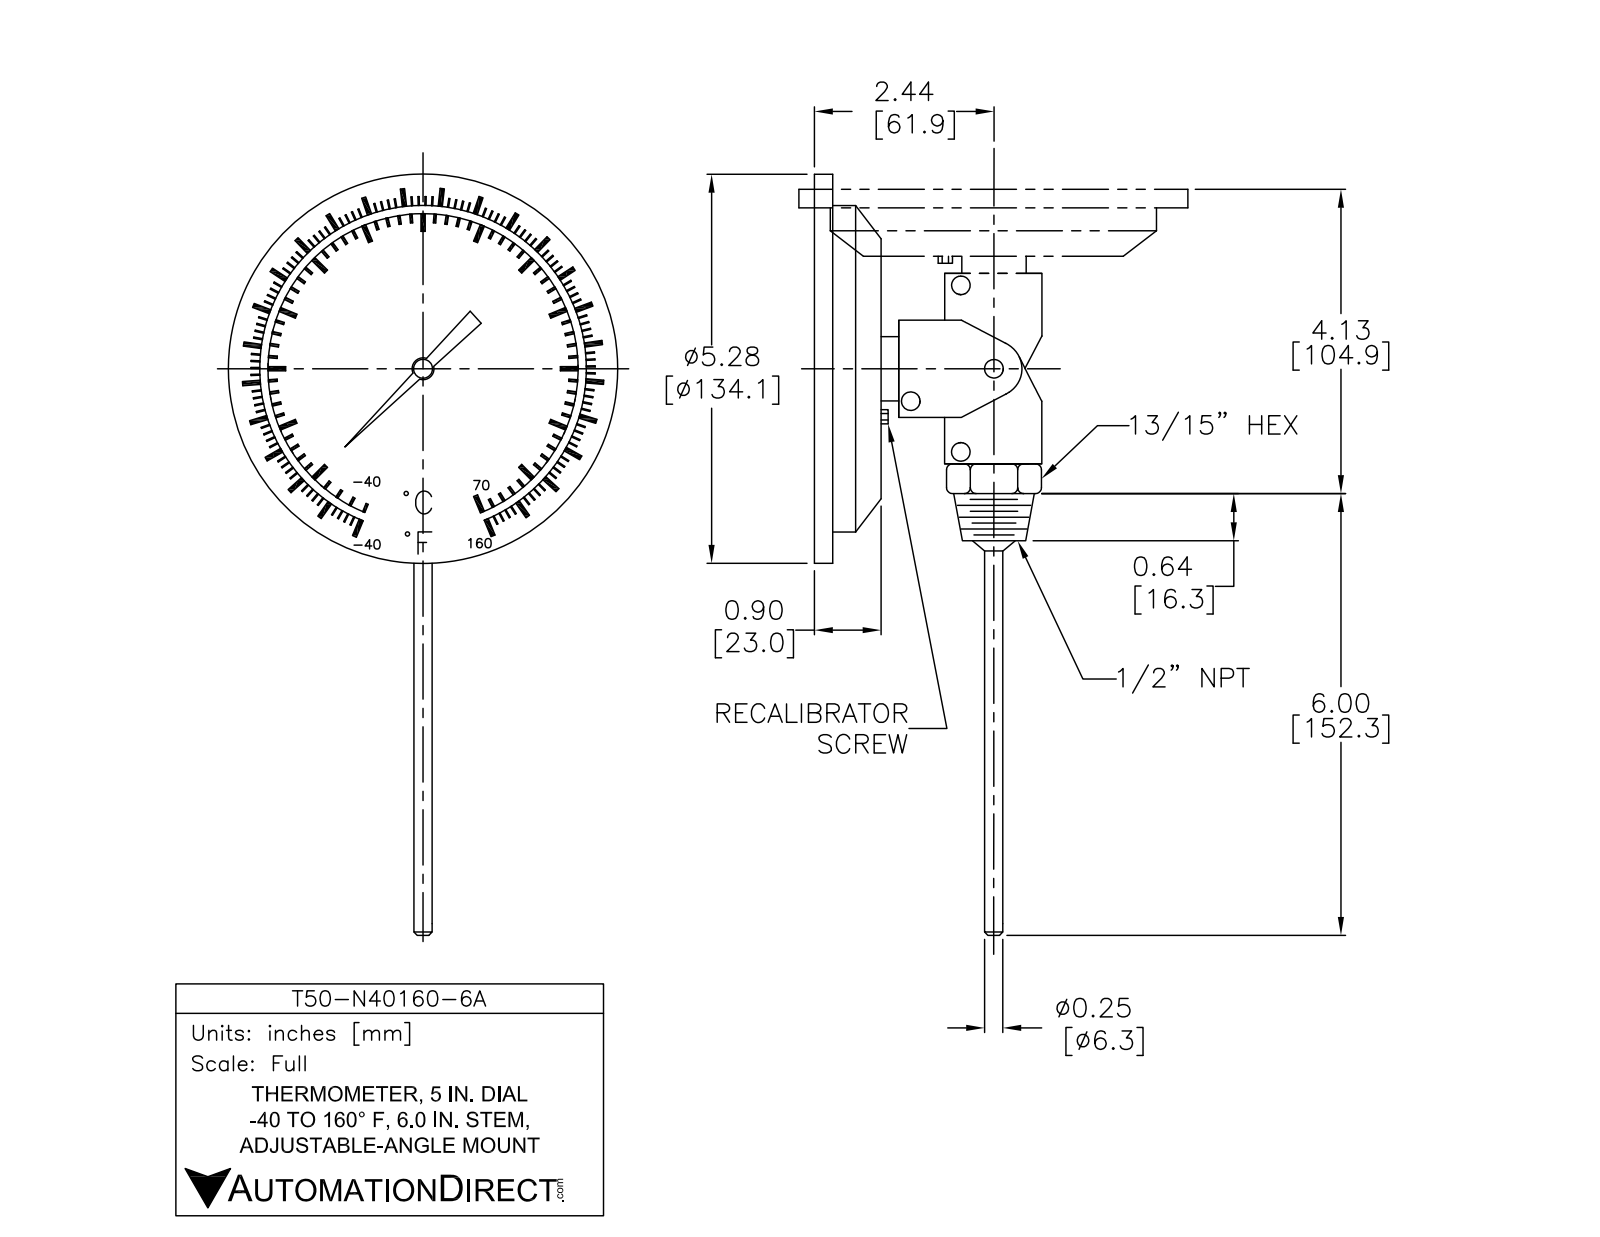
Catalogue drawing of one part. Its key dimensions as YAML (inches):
part_name: "T50-N40160-6A"
step_written_by: "SolidWorks 2021 (AUTOMOTIVE_DESIGN)"
units: inches
bodies: {solids: 1, faces: 499, planar: 310, cylindrical: 45, other: 144}
overall_size: [9.96, 5.28, 5.28]
volume: 10.23
surface_area: 98.37
round_holes:
  - {diameter: 3.424, count: 1}
  - {diameter: 3.7, count: 1}
  - {diameter: 4.76, count: 1}
  - {diameter: 4.836, count: 1}
round_bosses_or_shafts:
  - {diameter: 0.305, count: 4}
  - {diameter: 0.145, count: 2}
  - {diameter: 5.28, count: 1}
  - {diameter: 4.97, count: 1}
  - {diameter: 3.73, count: 1}
  - {diameter: 3.454, count: 1}
  - {diameter: 0.85, count: 1}
  - {diameter: 0.821, count: 1}
partial_cylinders:
  - {radius: 0.06, count: 10}
  - {radius: 0.04, count: 4}
  - {radius: 0.17, count: 1}
  - {radius: 0.336, count: 1}
  - {radius: 0.336, count: 1}
  - {radius: 0.342, count: 1}
  - {radius: 0.4, count: 1}
face_to_face_distances: [0.353, 0.074, 0.055, 0.427, 1.19, 0.815, 0.462, 0.388, 1.245, 2.435]
